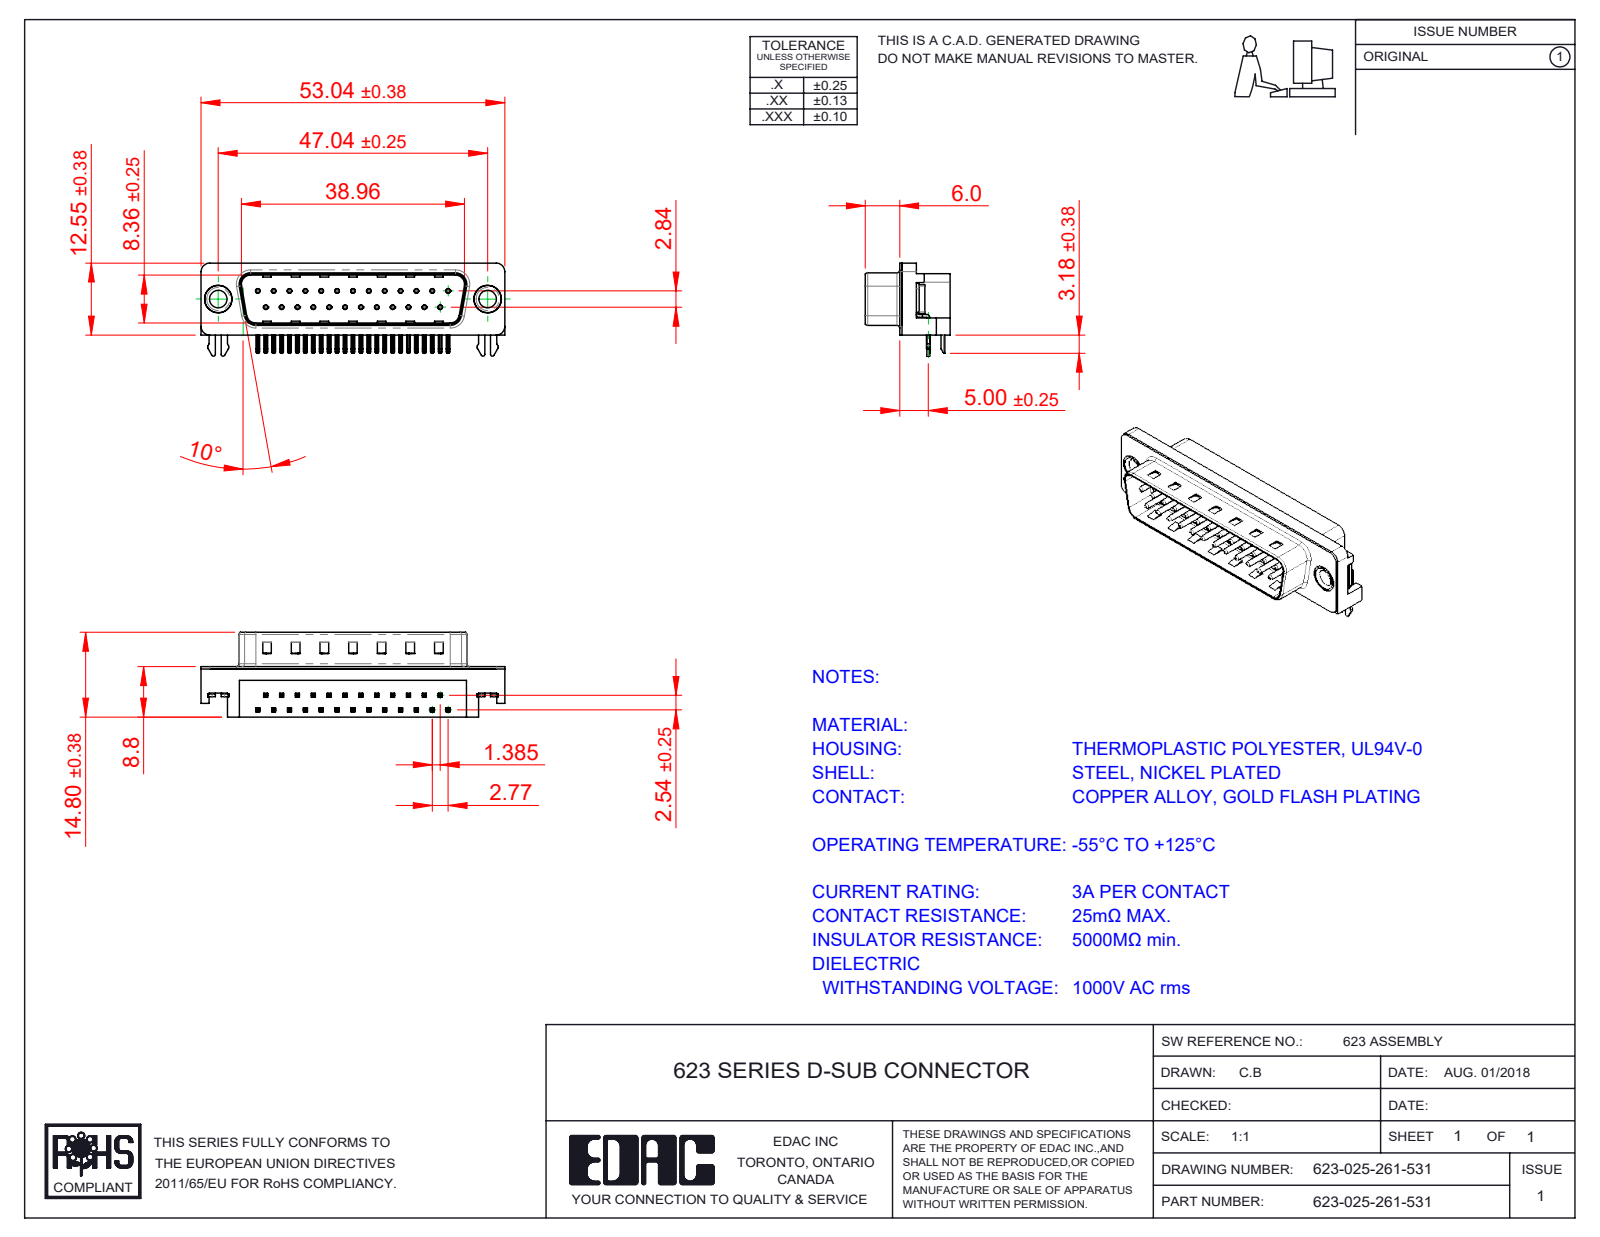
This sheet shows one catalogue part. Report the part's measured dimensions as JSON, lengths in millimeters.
{"part_name": "623-025-261-531; 623 Contact Top; 623 Housing_25 Socket; 623 2 Prong Board Lock (+3 more)", "step_written_by": "SolidWorks 2016 (CONFIG_CONTROL_DESIGN)", "units": "millimeters", "bodies": {"solids": 31, "faces": 2245, "planar": 1433, "cylindrical": 635, "other": 177}, "overall_size": [53.04, 16.25, 14.8], "volume_mm3": 4721, "surface_area_mm2": 6755, "round_holes": [[0.35, 25], [0.8, 25], [3.05, 2], [4, 2], [4.8, 2], [5, 2]], "round_bosses_or_shafts": [[0.75, 25], [4.9, 2], [4.75, 2], [3.85, 2]], "partial_cylinders_radius": [[0.25, 108], [0.12, 50], [0.5, 14], [1, 8], [1.5, 7], [0.32, 4], [0.9, 4], [1.6, 4]], "face_to_face_distances": [0.4, 8.4, 2.1, 1.7, 8.76, 10.46, 10.86, 10.35, 8.8, 5.9], "hole_center_spacings": [3.16, 2.77, 11.08, 5.54, 8.31, 5.03, 13.85, 7.48]}
